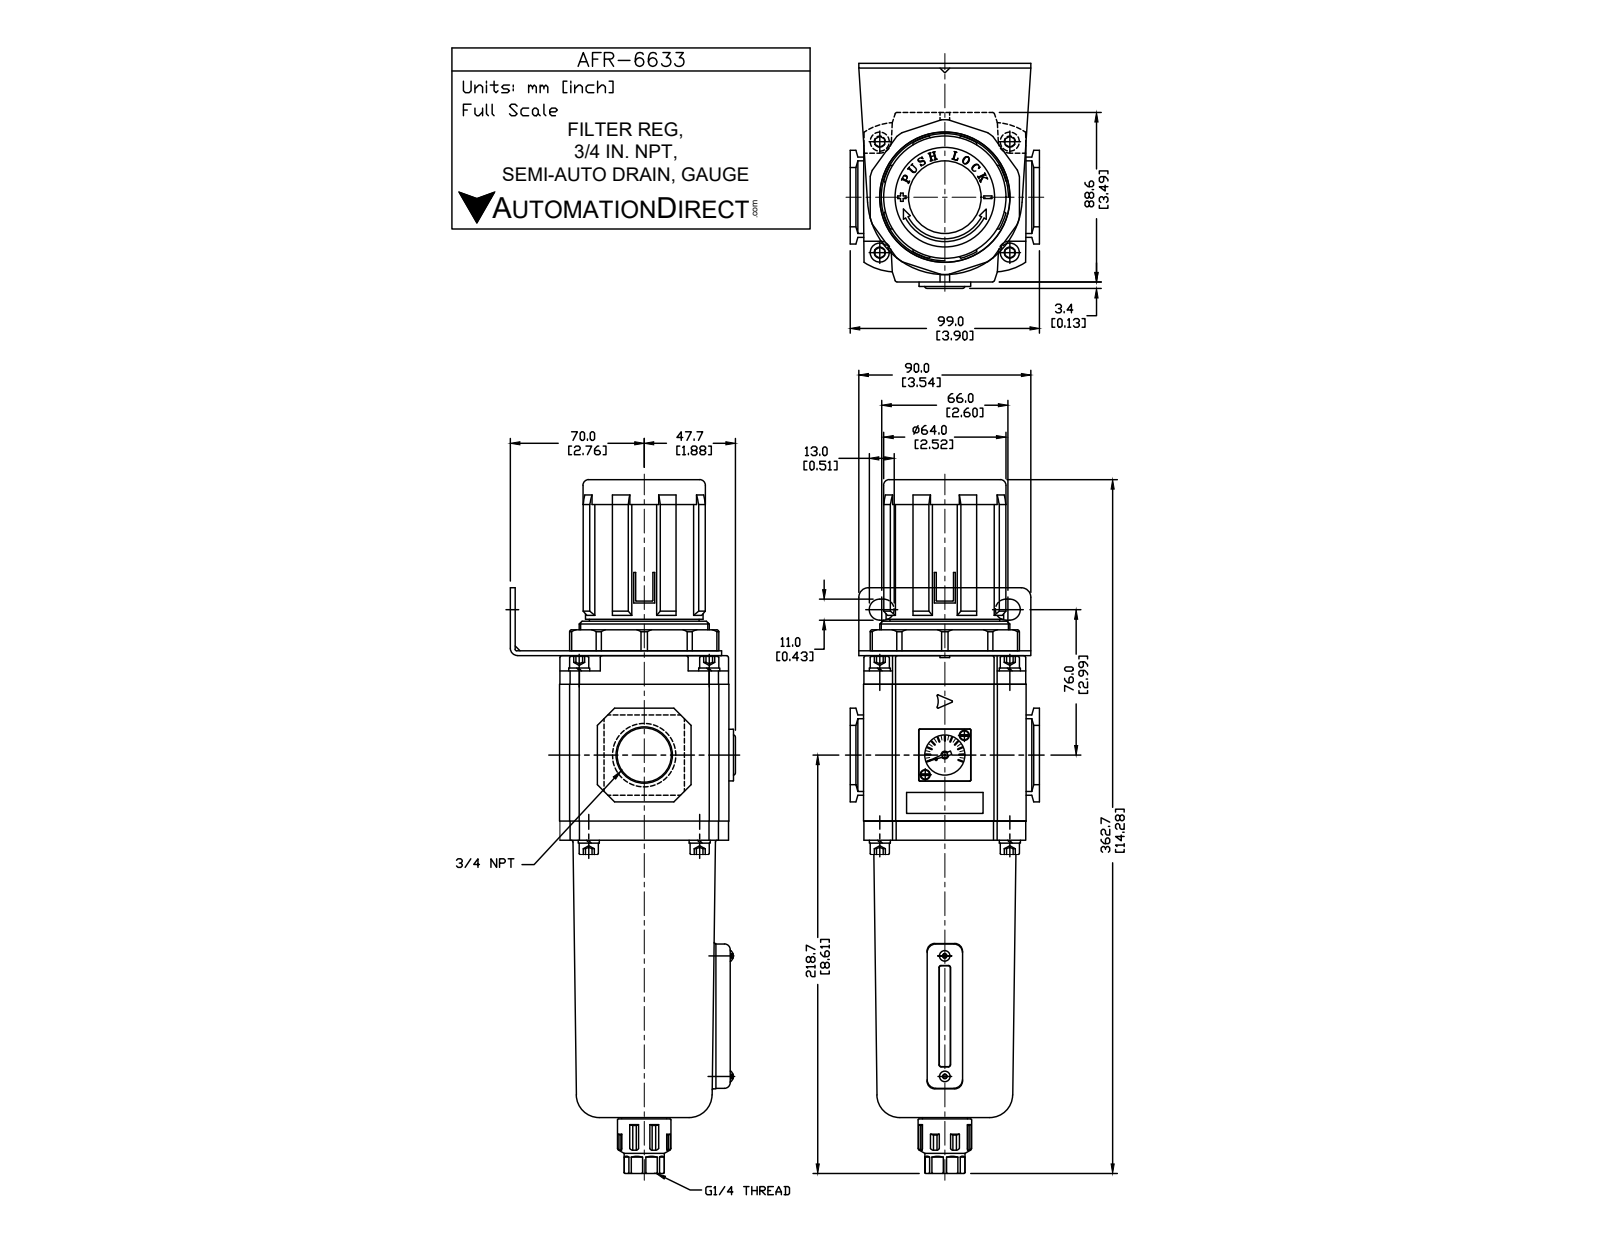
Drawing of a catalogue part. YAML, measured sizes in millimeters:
part_name: "AFR-6633"
step_written_by: "SolidWorks 2015 (CONFIG_CONTROL_DESIGN)"
units: millimeters
bodies: {solids: 16, faces: 703, planar: 439, cylindrical: 175, other: 89}
overall_size: [362.7, 117, 99]
volume: 1686000
surface_area: 184625
round_holes:
  - {diameter: 3, count: 6}
  - {diameter: 2, count: 1}
  - {diameter: 12, count: 1}
  - {diameter: 23.01, count: 1}
  - {diameter: 30, count: 1}
  - {diameter: 38, count: 1}
round_bosses_or_shafts:
  - {diameter: 10, count: 8}
  - {diameter: 5.5, count: 2}
  - {diameter: 2.7, count: 2}
  - {diameter: 68, count: 1}
  - {diameter: 64, count: 1}
  - {diameter: 62, count: 1}
  - {diameter: 53.76, count: 1}
  - {diameter: 28, count: 1}
partial_cylinders:
  - {radius: 1, count: 12}
  - {radius: 1.2, count: 10}
  - {radius: 1.3, count: 8}
  - {radius: 2.5, count: 8}
  - {radius: 9.5, count: 8}
  - {radius: 19.9, count: 8}
  - {radius: 0.5, count: 6}
  - {radius: 0.3, count: 4}
face_to_face_distances: [2.5, 91.2, 88.7, 87.6, 1, 88.6, 92, 85, 10, 7]
hole_center_spacings: [41.35, 34.68, 53.16, 63.36, 82.71, 69.35]
